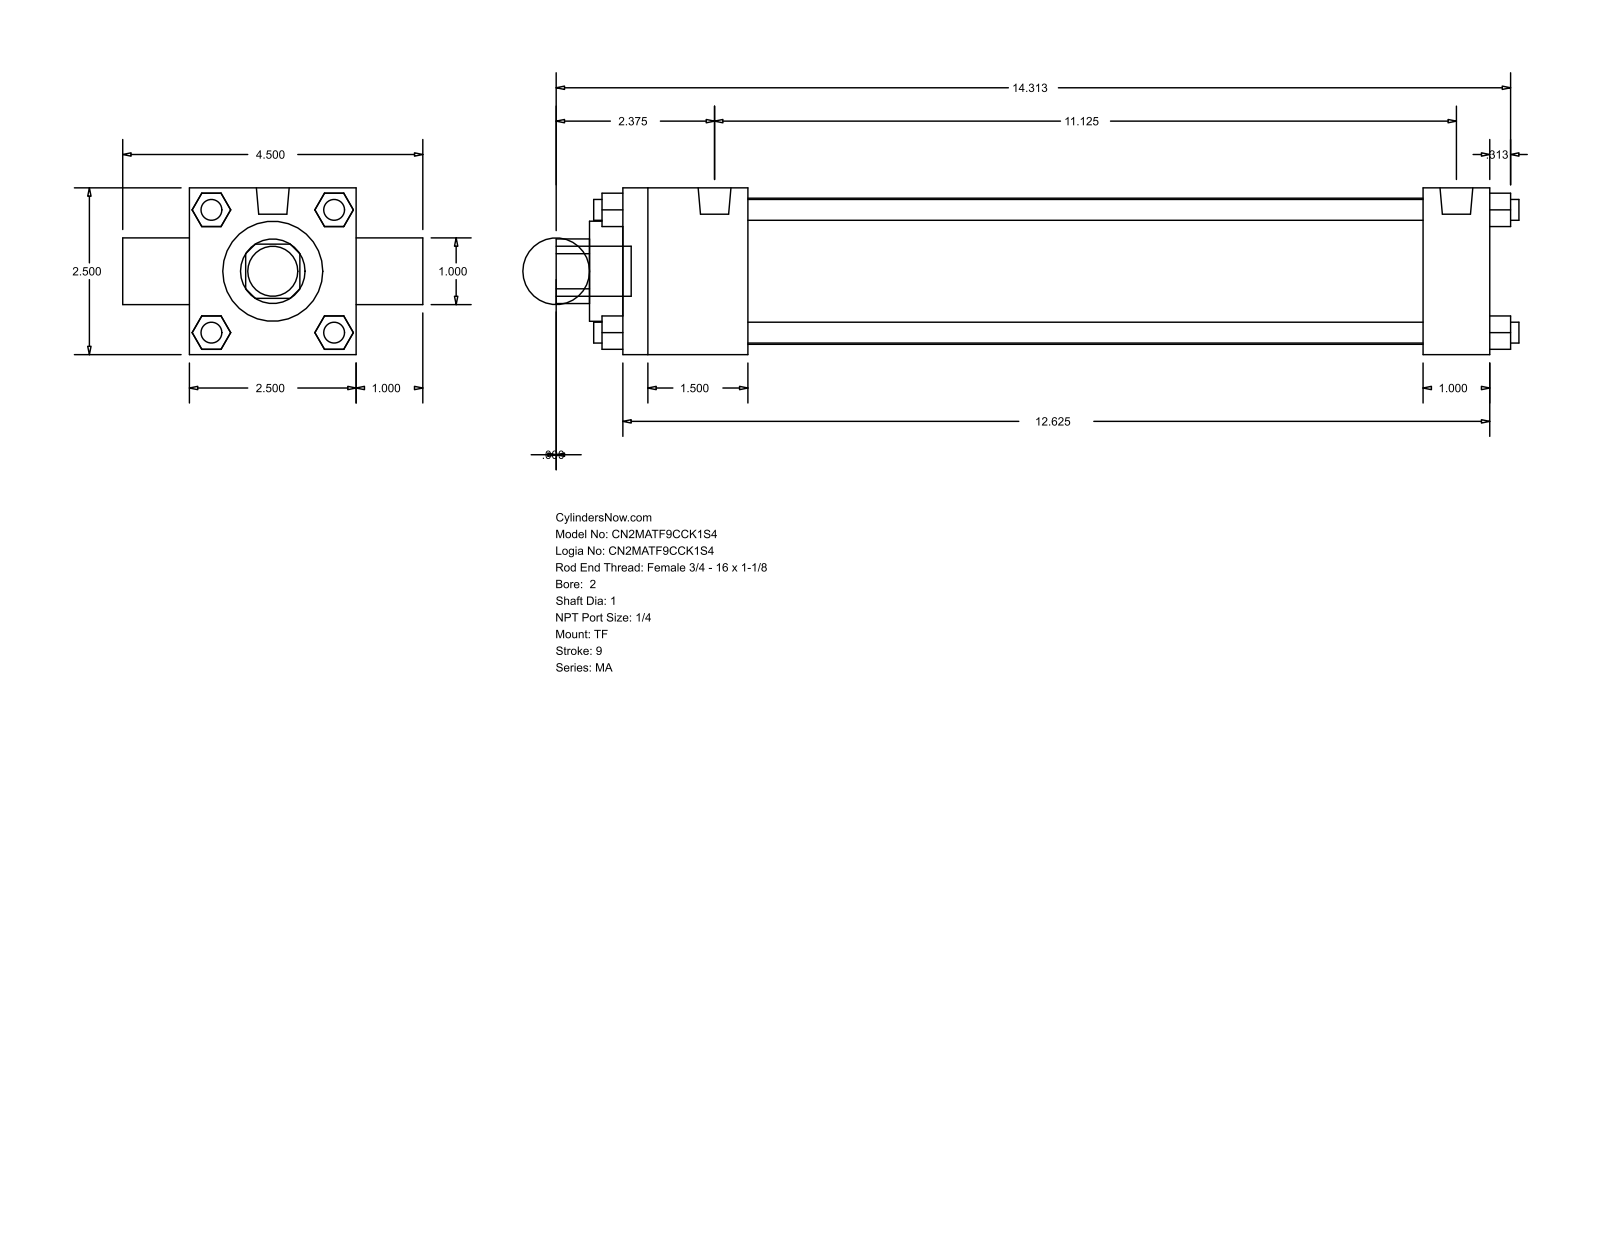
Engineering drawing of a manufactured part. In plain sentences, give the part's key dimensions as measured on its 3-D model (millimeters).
The part is named "MA_TF__0200_1". Its 3-D file was written by "GSSL Pune (CONFIG_CONTROL_DESIGN)". It is 0 solids with 120 faces: 92 planar, 28 cylindrical and 0 other. Overall it measures 366.71 by 114.3 by 63.5 millimeters. Round holes: 2 of diameter 25.4, 1 of diameter 38.1, 1 of diameter 55.63. Round bosses or shafts: 7 of diameter 7.94, 2 of diameter 12.49, 1 of diameter 19.05. Partial cylindrical surfaces (rounded edges, fillets, slot ends): 1 of radius 12.29. The main face-to-face distances are 63.5, 25.4, 330.2, 12.7, 47.63, 304.8, 257.17, 282.57, 88.9, 40.47.
